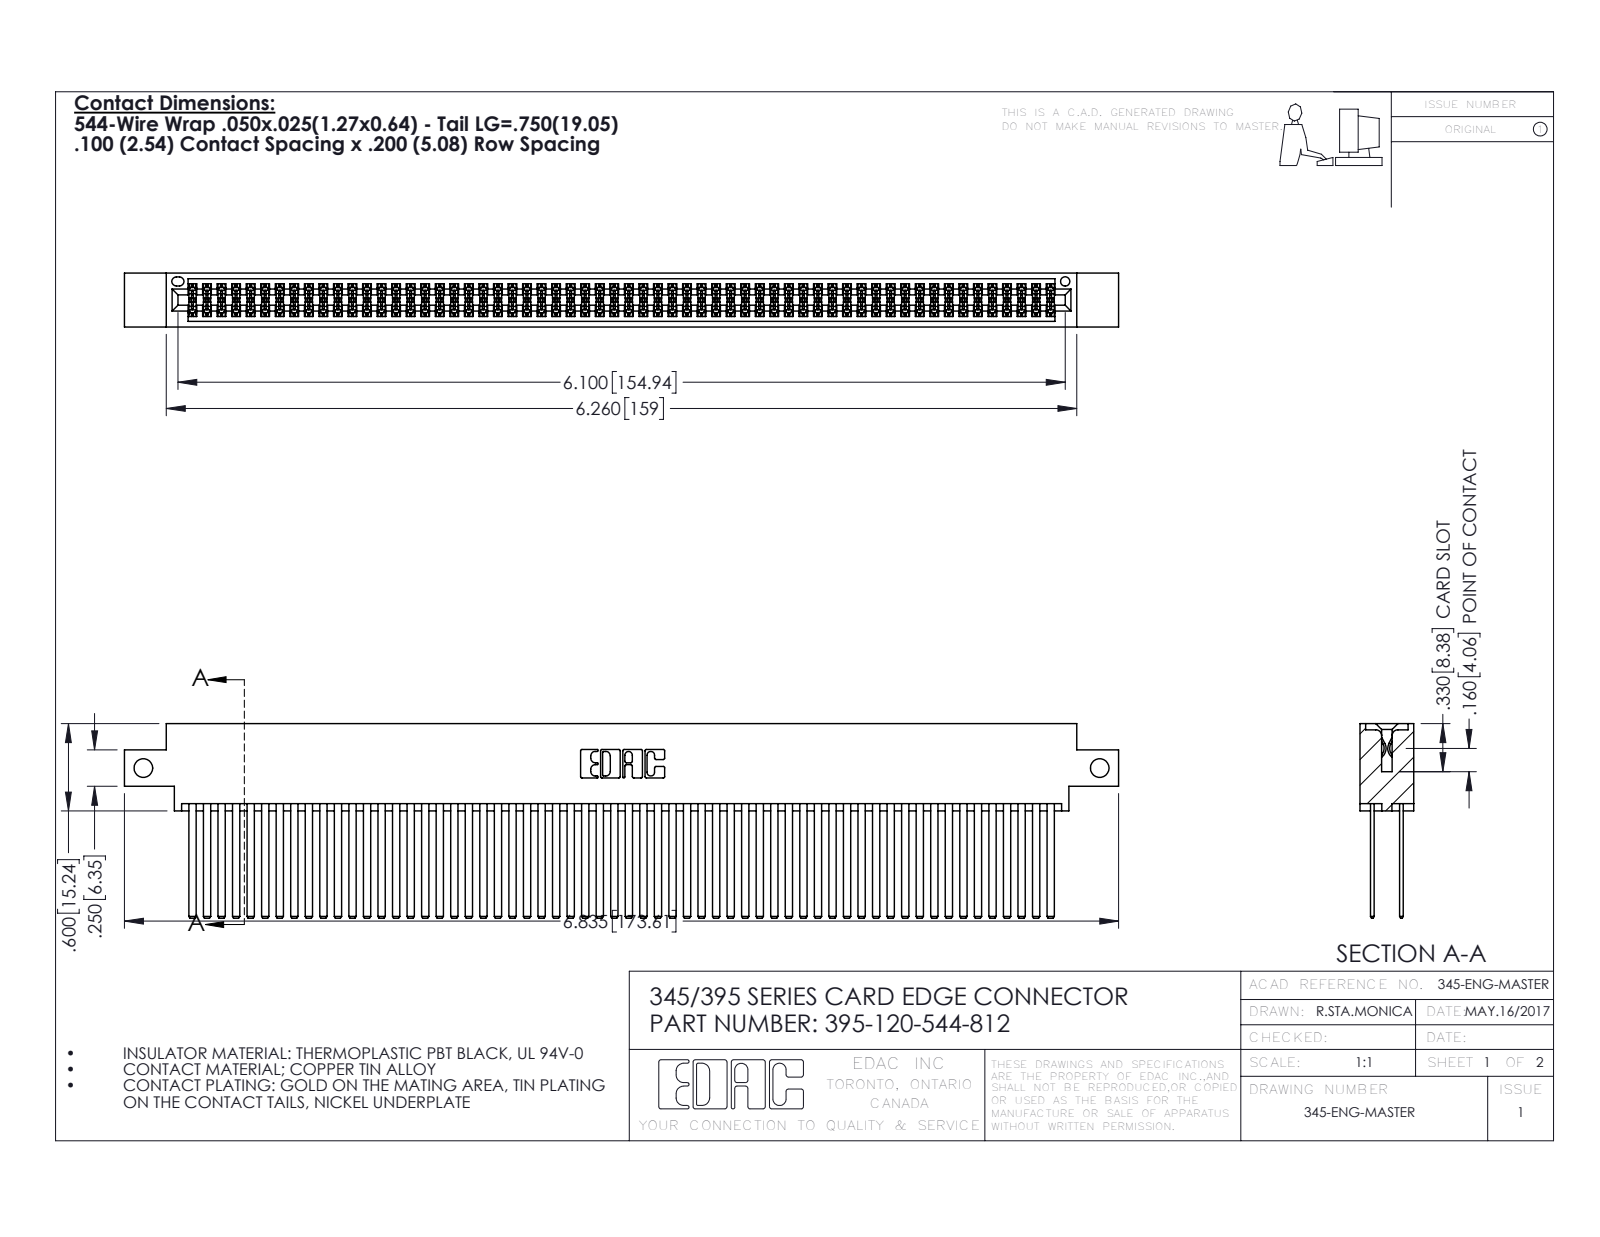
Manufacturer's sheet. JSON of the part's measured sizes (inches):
{"part_name": "345-292-001_345-293-144; 345 Part_0.170 Offset - Side Mount; 395-120-544-812", "step_written_by": "SolidWorks 2016 (CONFIG_CONTROL_DESIGN)", "units": "inches", "bodies": {"solids": 121, "faces": 5410, "planar": 3564, "cylindrical": 1846, "other": 0}, "overall_size": [6.835, 1.337, 0.37], "volume_in3": 1.13, "surface_area_in2": 50.61, "round_holes": [[0.128, 2], [0.064, 1]], "partial_cylinders_radius": [[0.006, 180], [0.01, 22], [0.007, 6], [0.031, 6], [0.026, 3], [0.014, 2], [0.019, 2], [0.022, 2]], "face_to_face_distances": [0.2, 0.025, 0.072, 0.098, 0.272, 0.298, 0.225, 0.175, 0.37, 0.15], "hole_center_spacings": [6.575]}
